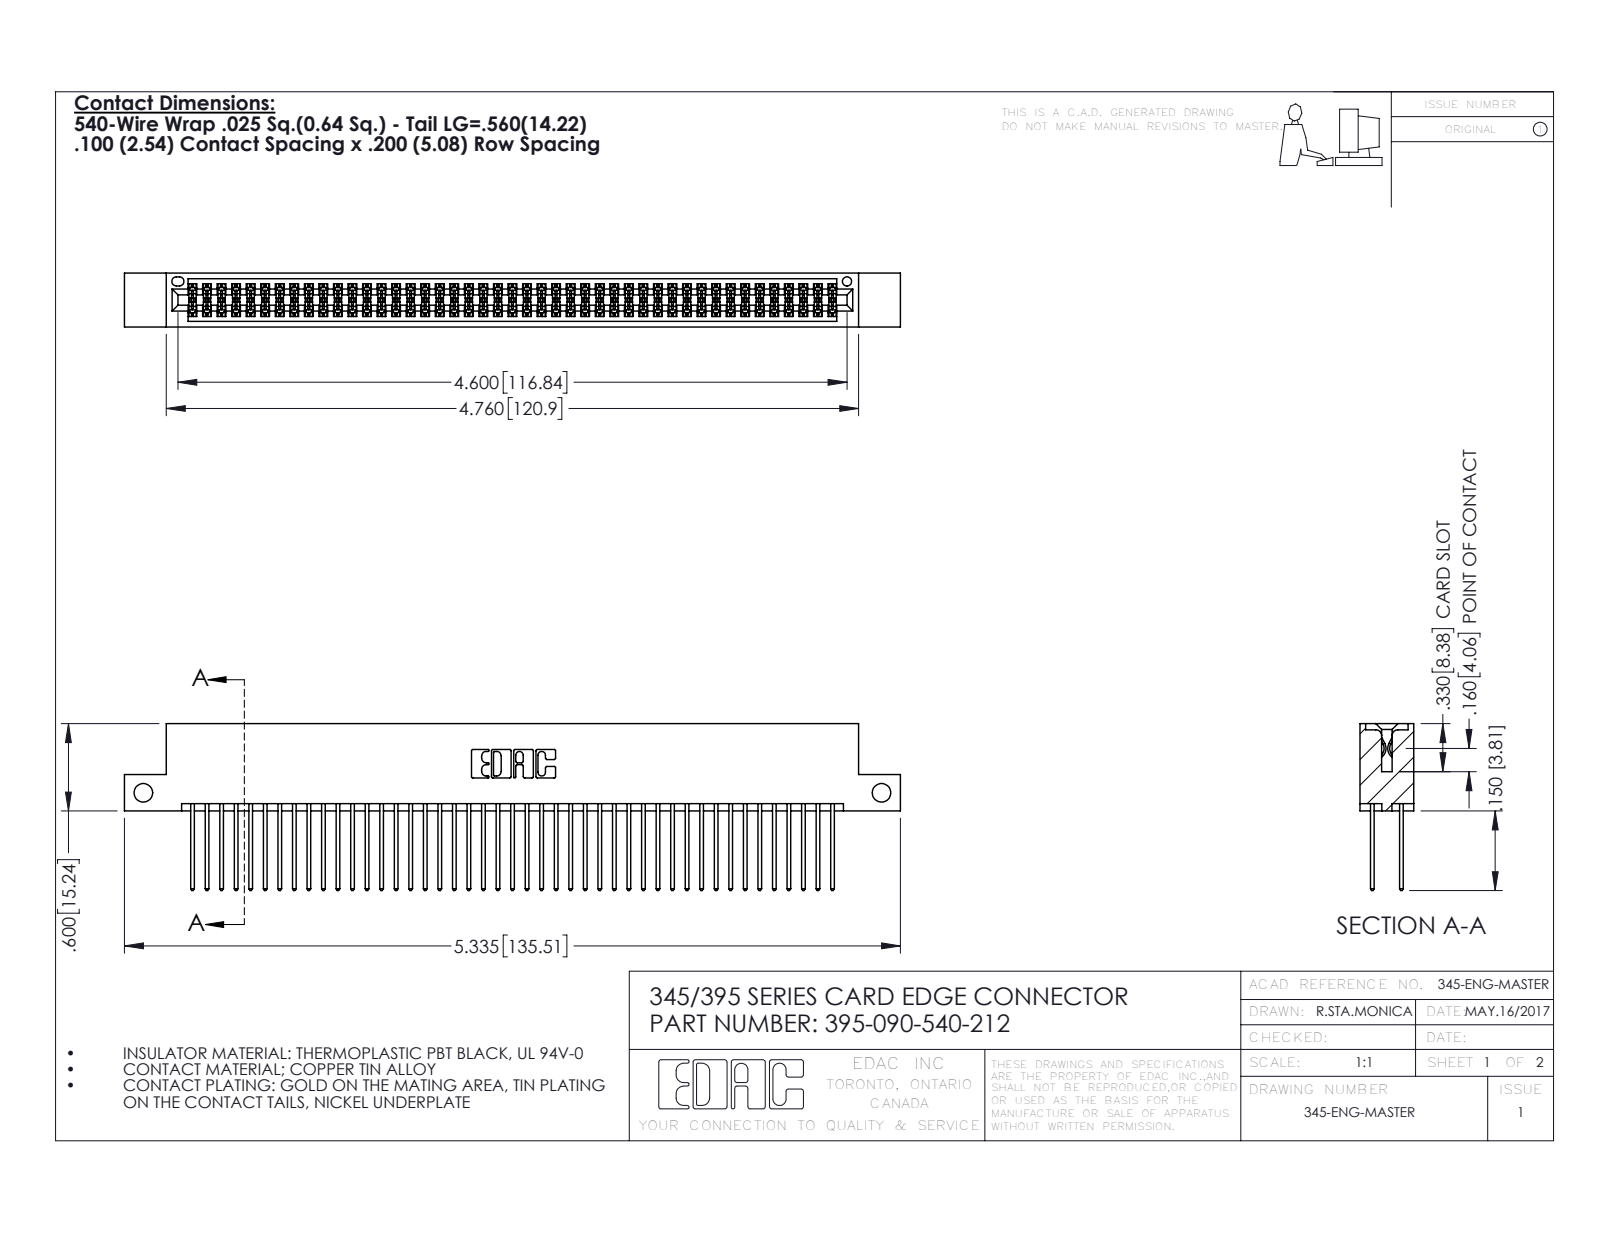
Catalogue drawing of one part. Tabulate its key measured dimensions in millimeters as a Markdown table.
| quantity | value |
| --- | --- |
| part name | 345 Part_Flush Mounting Lugs - Side Mount; 345-292-001_345-293-140; 395-090-540-212 |
| STEP written by | SolidWorks 2016 (CONFIG_CONTROL_DESIGN) |
| units | millimeters |
| bodies | 91 solids, 4626 faces (3050 planar, 1576 cylindrical, 0 other) |
| overall size | 135.5 × 29.1 × 9.4 |
| volume | 13 400 mm³ |
| surface area | 21 380 mm² |
| round holes (diameter × count) | 3.3 × 2, 1.6 × 1 |
| partial cylindrical surfaces (radius × count) | 0.2 × 135, 0.3 × 90, 0.3 × 22, 0.2 × 6, 0.8 × 6, 0.7 × 3, 0.4 × 2, 0.5 × 2 |
| main face-to-face distances | 7.6, 1.8, 5.1, 2.5, 6.9, 0.6, 9.4, 5.7, 4.4, 3.8 |
| hole center spacings | 128.9 |
